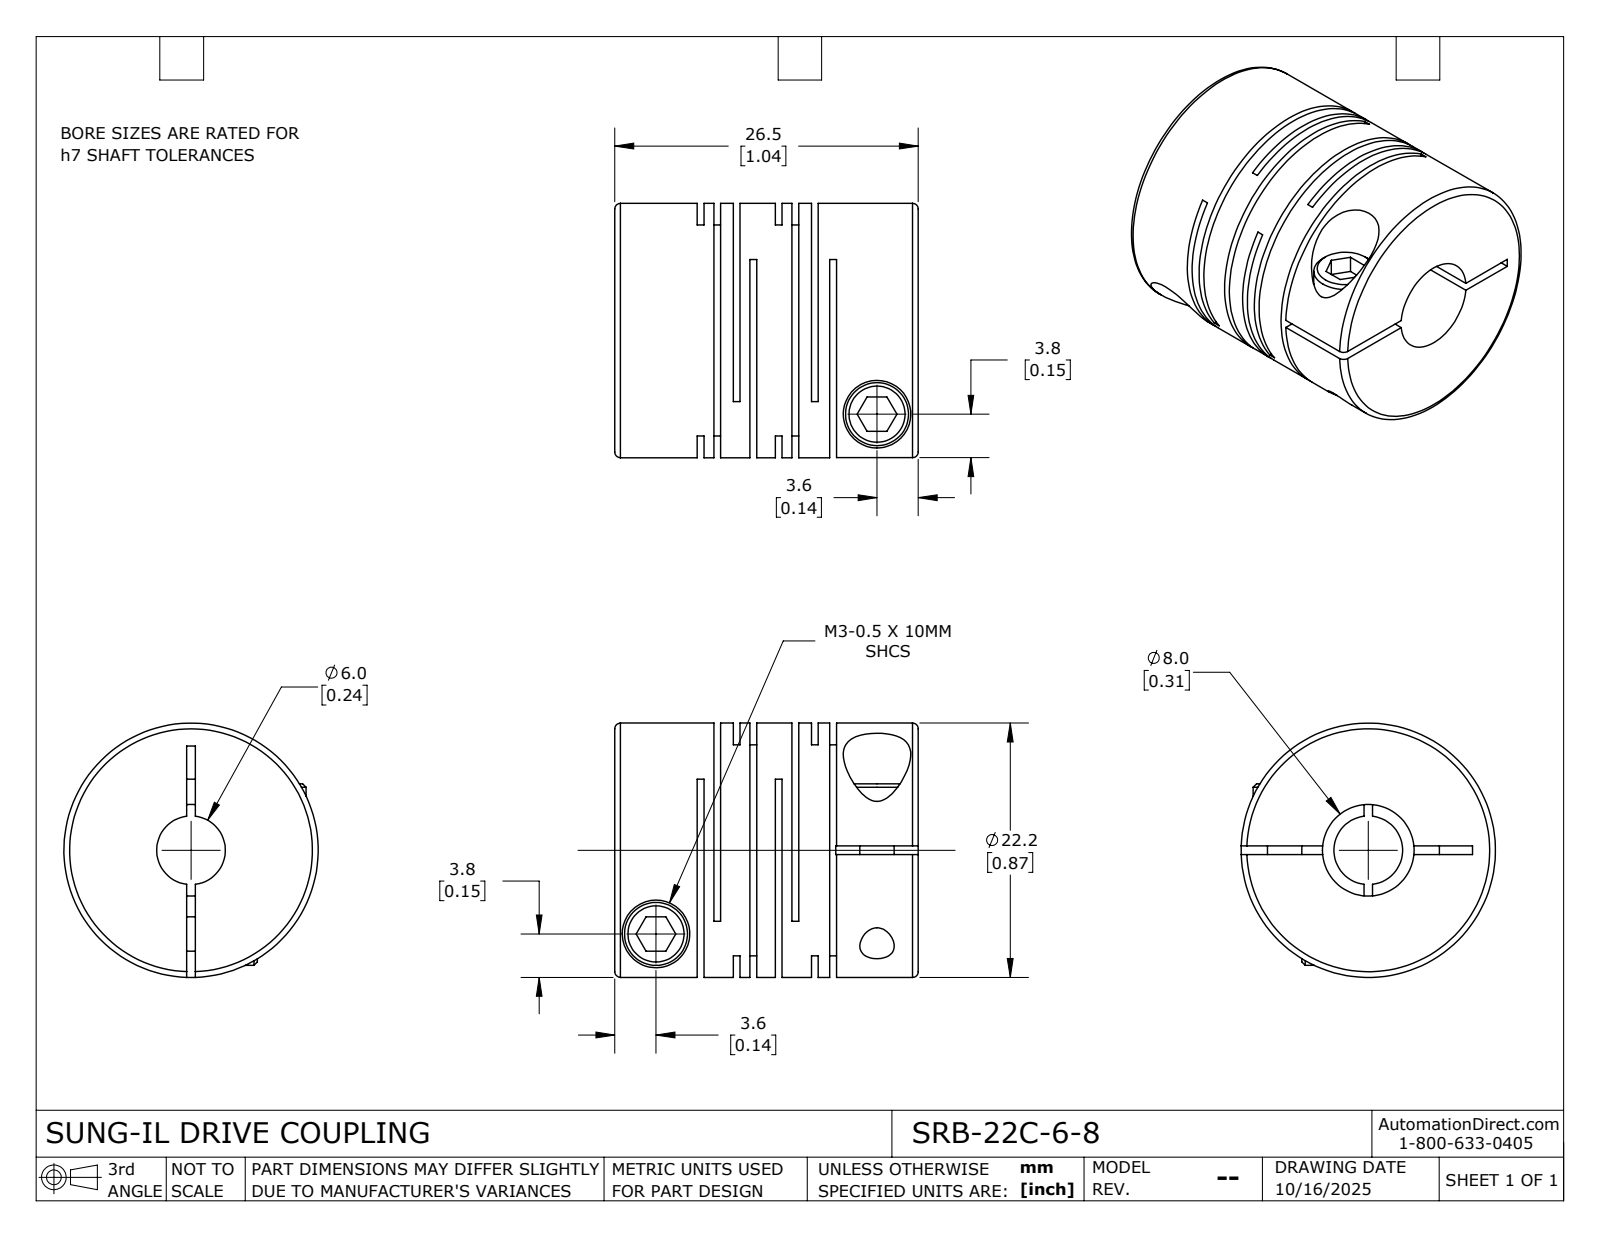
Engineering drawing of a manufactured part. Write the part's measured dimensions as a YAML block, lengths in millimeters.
part_name: "SRB-22C-6-8"
step_written_by: "SolidWorks 2024 (CONFIG_CONTROL_DESIGN)"
units: millimeters
bodies: {solids: 1, faces: 115, planar: 60, cylindrical: 42, other: 13}
overall_size: [26.5, 22.2, 22.2]
volume: 7464
surface_area: 7865
round_holes:
  - {diameter: 3, count: 2}
  - {diameter: 5.9, count: 2}
  - {diameter: 6, count: 1}
  - {diameter: 8, count: 1}
round_bosses_or_shafts:
  - {diameter: 5.5, count: 2}
  - {diameter: 22.2, count: 1}
face_to_face_distances: [0.59, 6.82, 1.45, 3.15, 5.37, 1.7, 3.67, 2.04, 7.41, 6.23]
